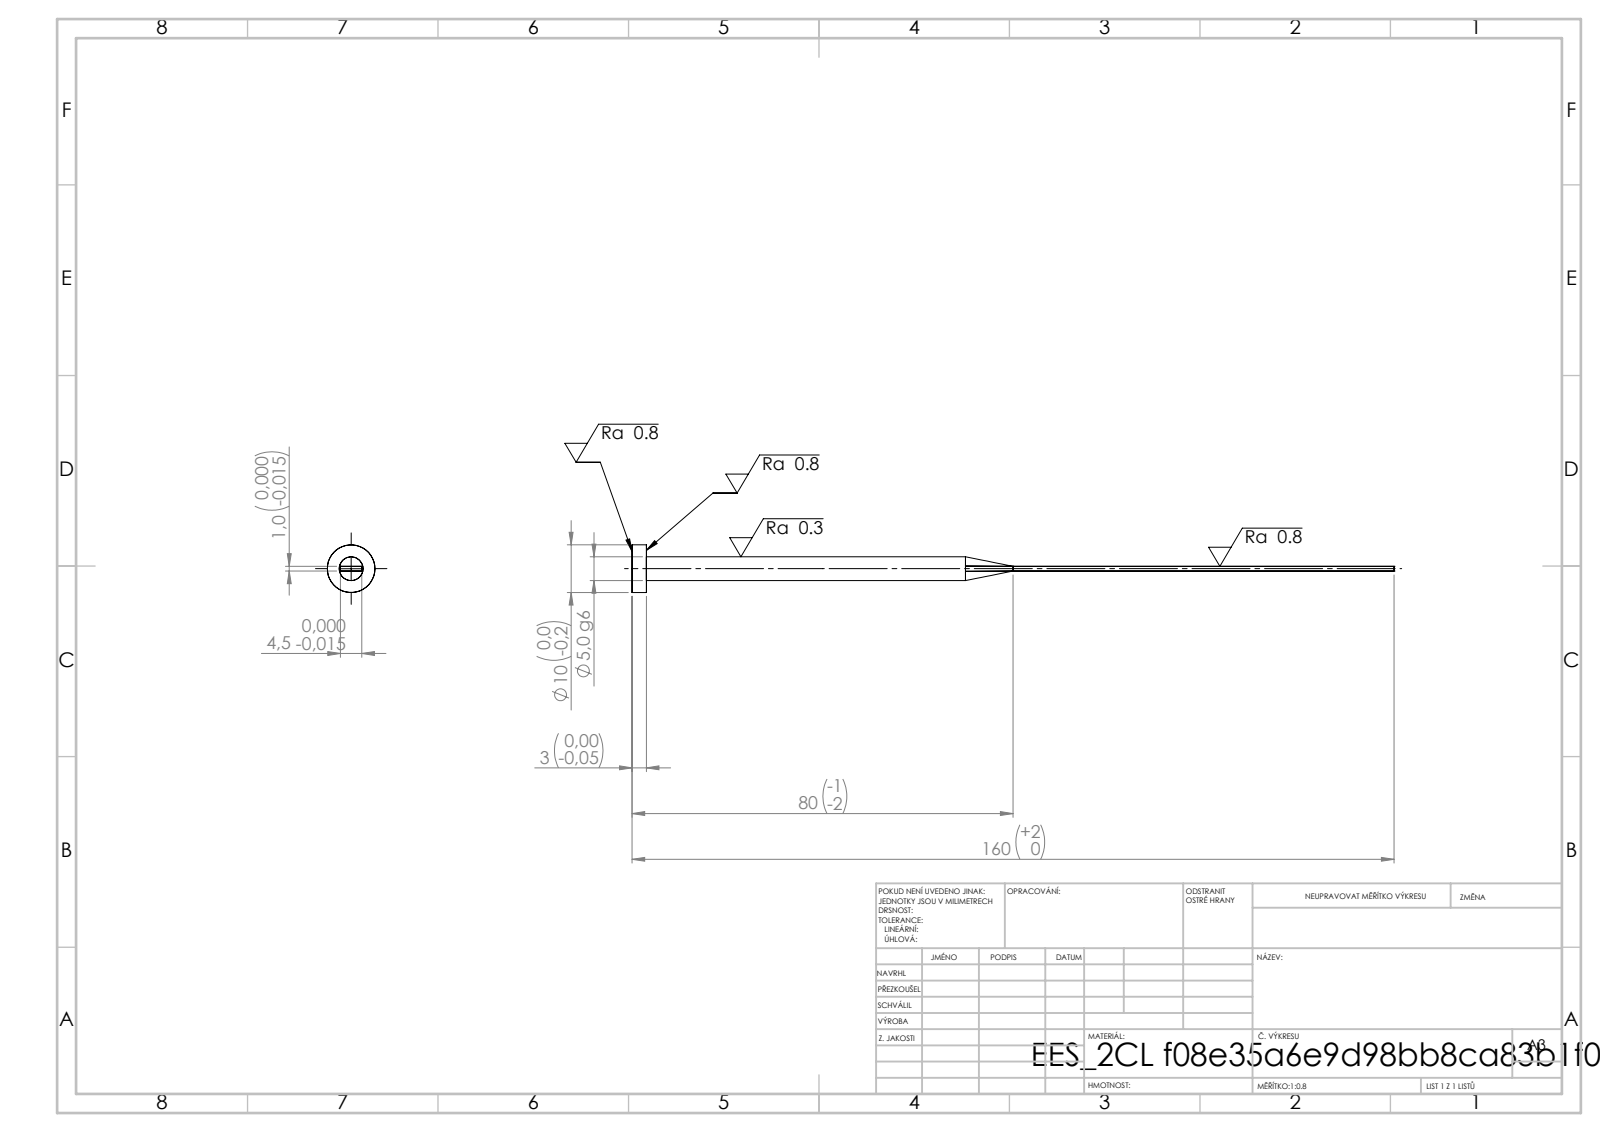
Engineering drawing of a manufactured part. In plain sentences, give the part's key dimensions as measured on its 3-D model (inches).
Its 3-D file was written by "SolidWorks 2019 (CONFIG_CONTROL_DESIGN)". It is 1 solid with 15 faces: 7 planar, 4 cylindrical and 4 other. Overall it measures 6.299 by 0.394 by 0.394 inches. Its volume is 0.124 cubic inches and its surface area 3.562 square inches. Round bosses or shafts: 1 of diameter 0.394, 1 of diameter 0.197. The main face-to-face distances are 0.039, 0.177, 0.118, 6.299, 6.181.
